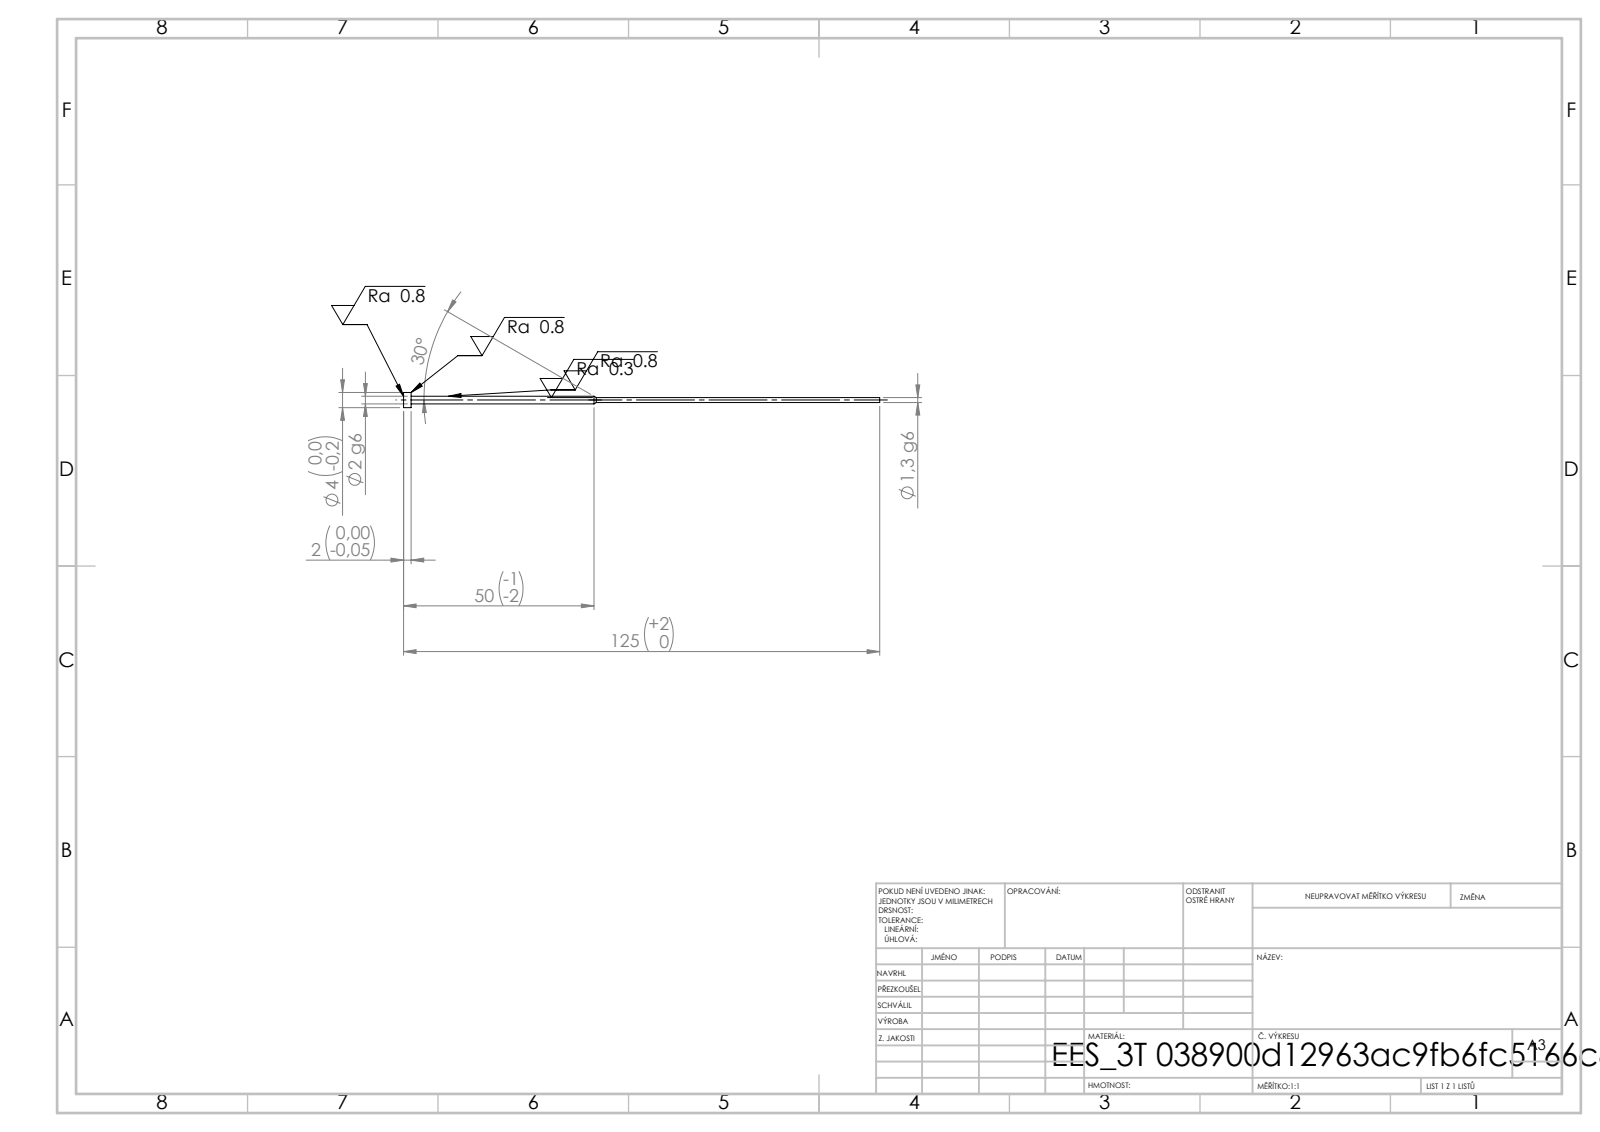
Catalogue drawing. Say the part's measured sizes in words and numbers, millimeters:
Its 3-D file was written by "SolidWorks 2019 (CONFIG_CONTROL_DESIGN)". It is 1 solid with 11 faces: 3 planar, 6 cylindrical and 2 other. Overall it measures 125 by 4 by 4 millimeters. Its volume is 276 cubic millimeters and its surface area 658 square millimeters. Round bosses or shafts: 1 of diameter 4, 1 of diameter 2, 1 of diameter 1.3. The main face-to-face distances are 2, 123, 125.
